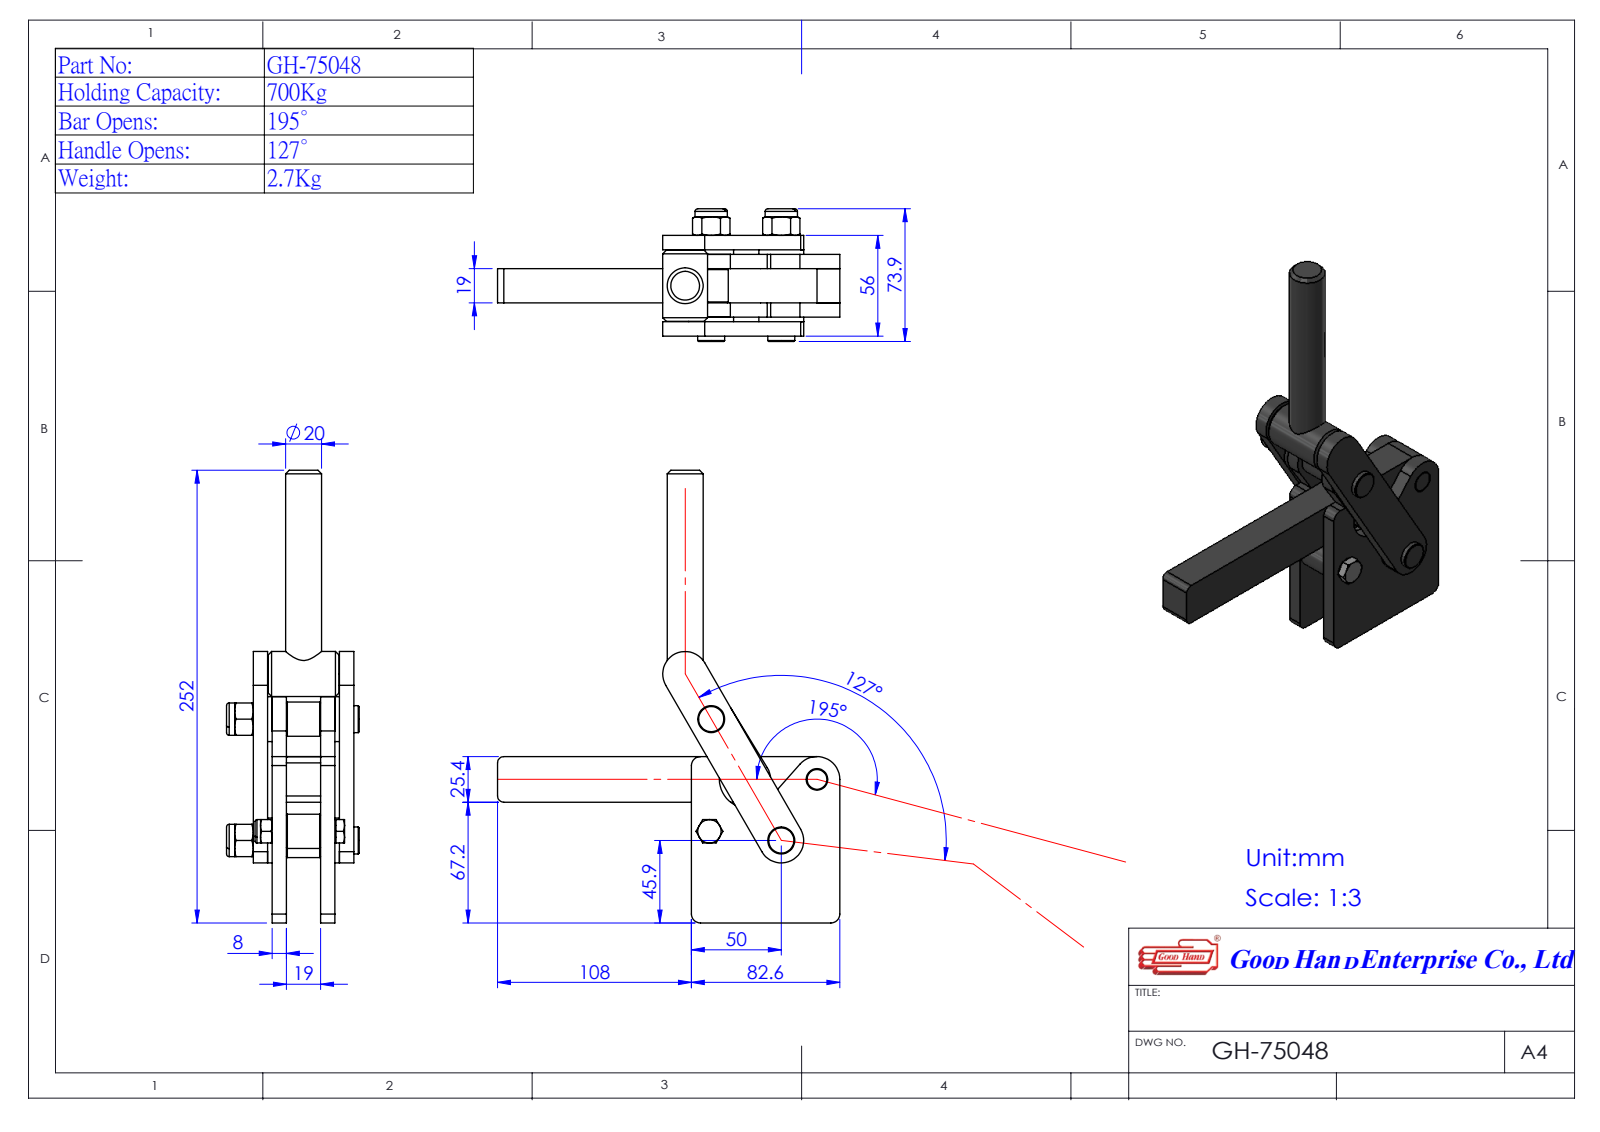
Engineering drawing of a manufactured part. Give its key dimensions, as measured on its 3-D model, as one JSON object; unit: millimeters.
{"part_name": "GH-75048(簡化); 4704808-1^GH-75048(簡化); Group4^GH-75048(簡化); Group2^GH-75048(簡化) (+1 more)", "step_written_by": "SolidWorks 2016 (AUTOMOTIVE_DESIGN)", "units": "millimeters", "bodies": {"solids": 4, "faces": 205, "planar": 83, "cylindrical": 69, "other": 53}, "overall_size": [252, 190.6, 69.37], "volume_mm3": 341850, "surface_area_mm2": 93939, "round_holes": [[9, 4], [12.8, 1]], "round_bosses_or_shafts": [[25, 3], [15, 3], [20, 1], [13, 1], [8.5, 1]], "partial_cylinders_radius": [[5, 3], [3.5, 2], [12.5, 1], [12.7, 1], [16, 1]], "face_to_face_distances": [8, 27, 19, 10.5, 37.5, 35, 18.5, 45.5, 48, 2.5], "hole_center_spacings": [36.06, 38.34, 38.68, 39.35, 39.4, 40.32, 62.46, 66.51]}
